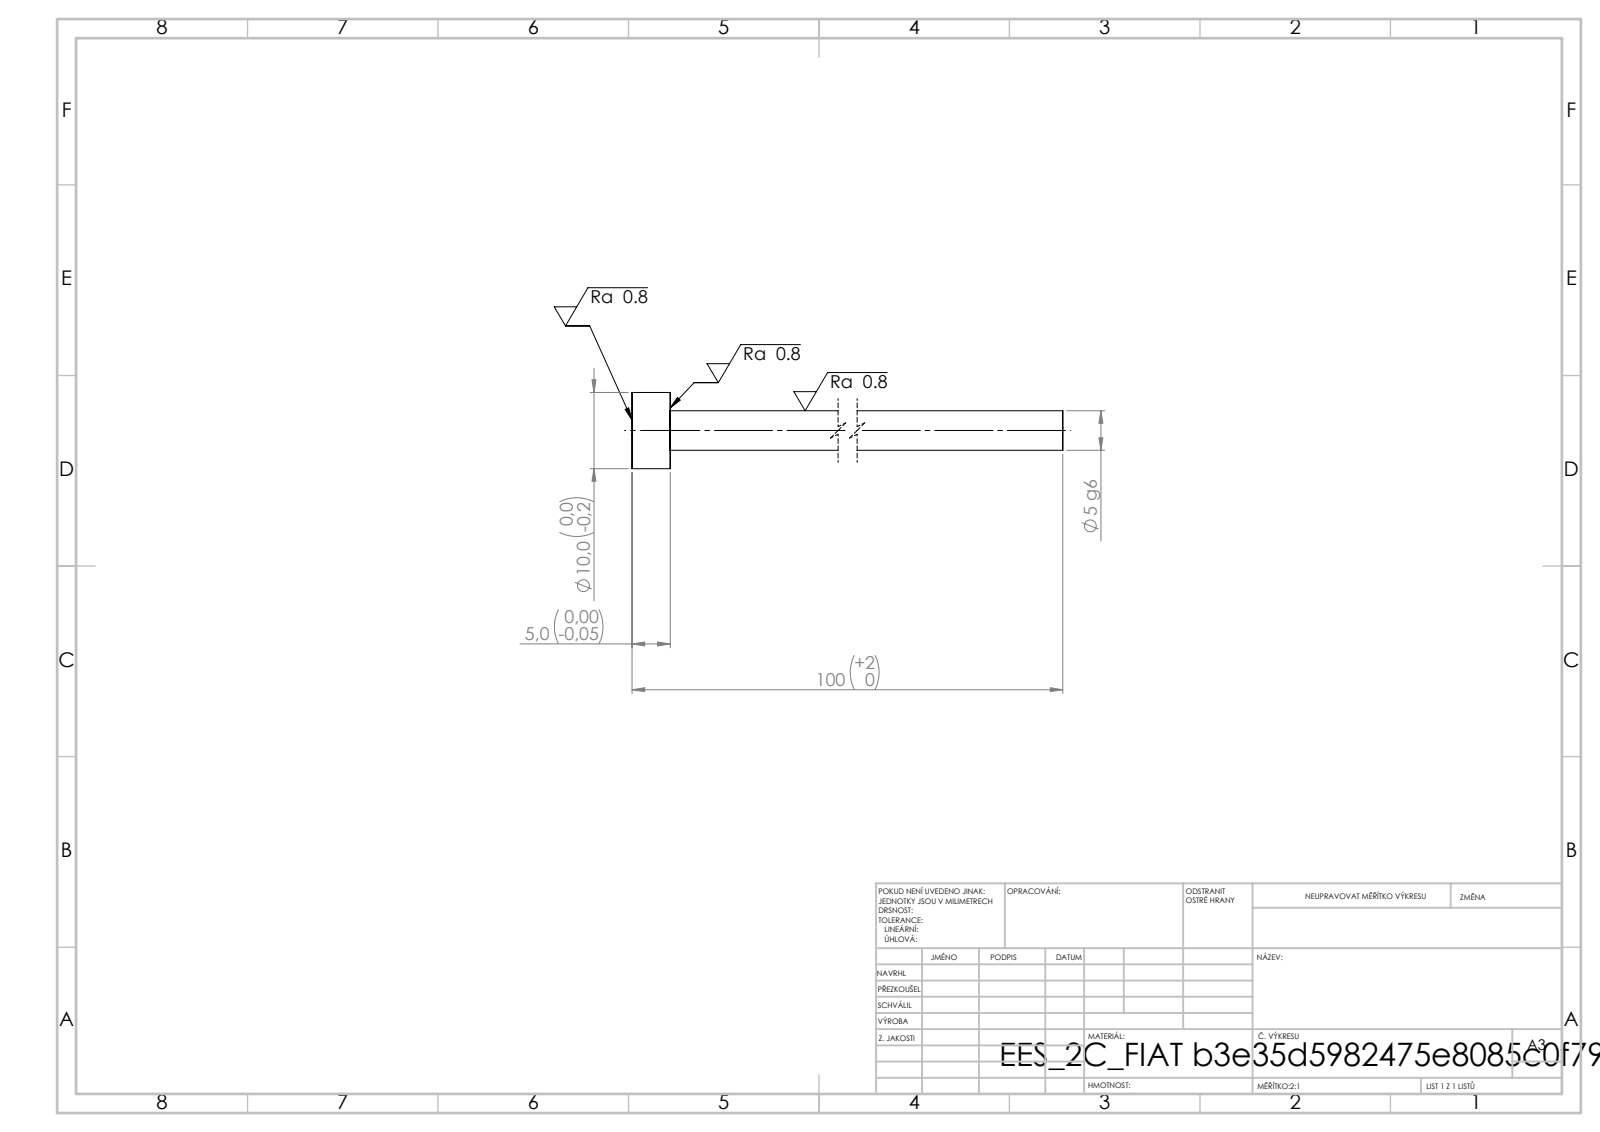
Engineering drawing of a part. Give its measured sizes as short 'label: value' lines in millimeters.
written by: SolidWorks 2019 (CONFIG_CONTROL_DESIGN)
unit: mm
bodies: 1 solid, 7 faces (3 planar, 4 cylindrical, 0 other)
size: 100 × 10 × 10
volume: 2 410 mm³; area: 1 866 mm²
bosses: 1× ⌀10, 1× ⌀5.2
face distances: 5, 100, 95
